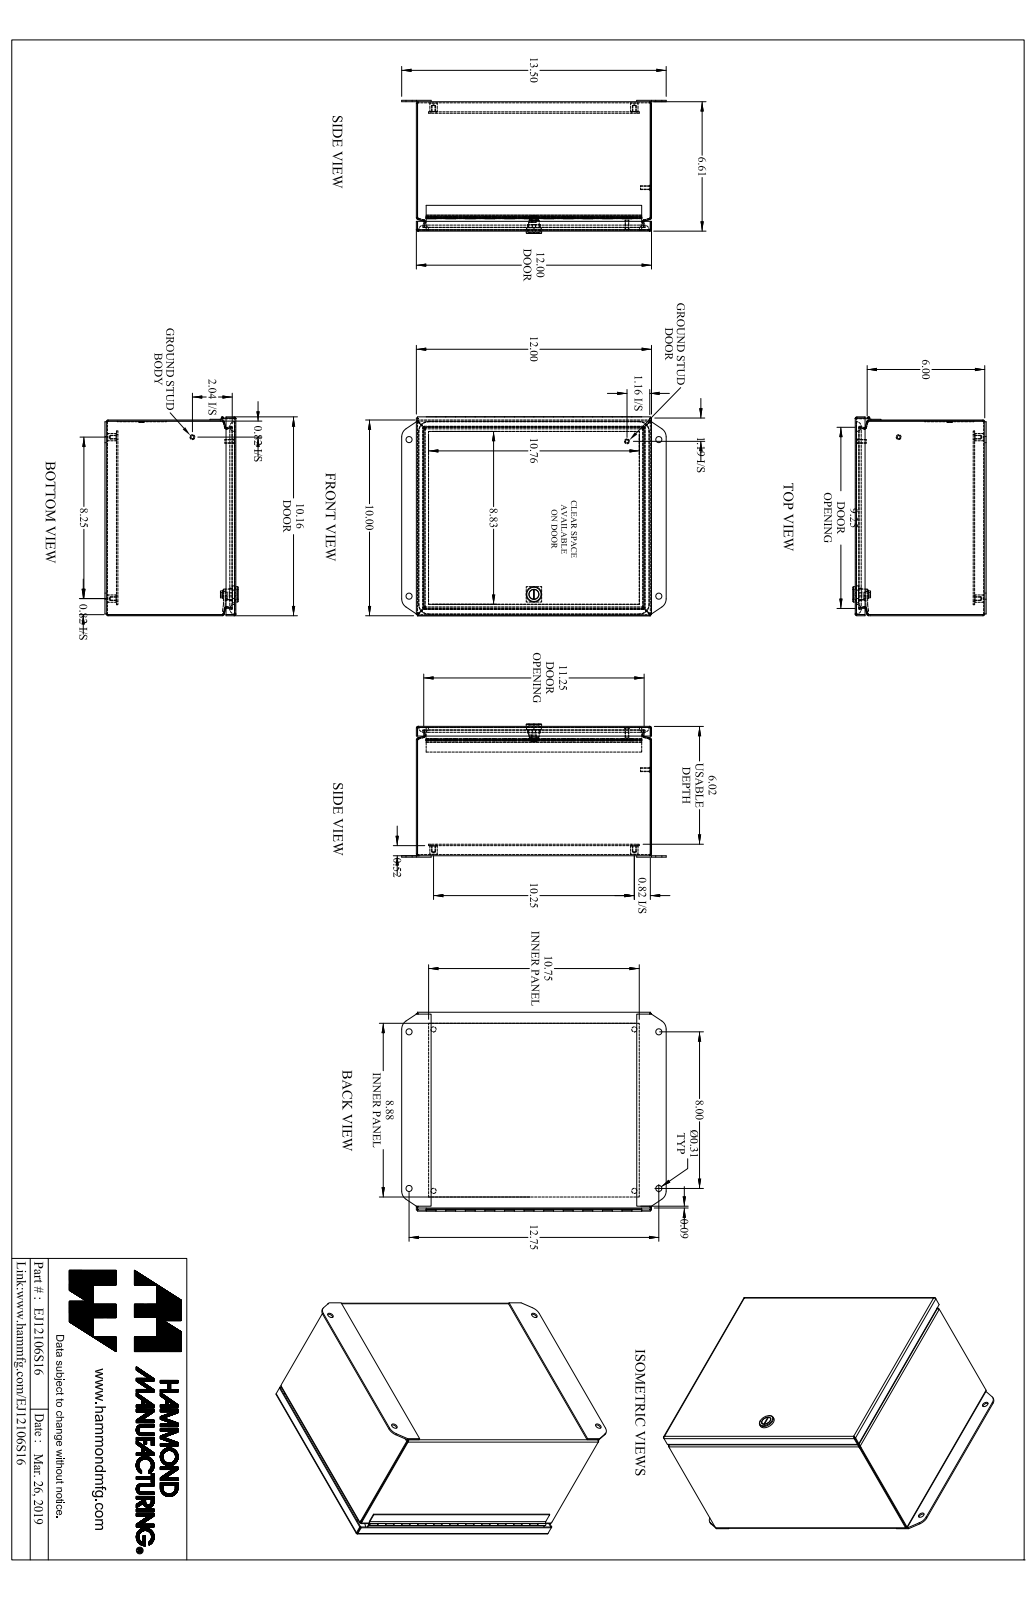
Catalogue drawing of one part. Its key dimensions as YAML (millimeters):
part_name: "EJ12106S16_Default"
step_written_by: "SolidWorks 2019 (CONFIG_CONTROL_DESIGN)"
units: millimeters
bodies: {solids: 16, faces: 628, planar: 326, cylindrical: 222, other: 80}
overall_size: [342.9, 258.2, 172.8]
volume: 738600
surface_area: 962600
round_holes:
  - {diameter: 4, count: 4}
  - {diameter: 6.7, count: 4}
  - {diameter: 8, count: 4}
  - {diameter: 1.3, count: 1}
  - {diameter: 13.1, count: 1}
round_bosses_or_shafts:
  - {diameter: 9.5, count: 4}
  - {diameter: 6.4, count: 2}
  - {diameter: 4.8, count: 2}
  - {diameter: 20, count: 1}
  - {diameter: 13.6, count: 1}
  - {diameter: 12.6, count: 1}
  - {diameter: 11, count: 1}
  - {diameter: 2.5, count: 1}
partial_cylinders:
  - {radius: 0.7, count: 16}
  - {radius: 2.2, count: 16}
  - {radius: 7.1, count: 12}
  - {radius: 6.4, count: 4}
  - {radius: 12.7, count: 4}
  - {radius: 12.7, count: 4}
  - {radius: 1.5, count: 2}
  - {radius: 0.8, count: 1}
face_to_face_distances: [1.4, 166.5, 252.6, 303.4, 1.8, 15, 167.9, 165, 154.8, 153.3]
hole_center_spacings: [31.9, 292.1, 357.7, 260.4, 208.8, 334.2, 130.3, 162]
